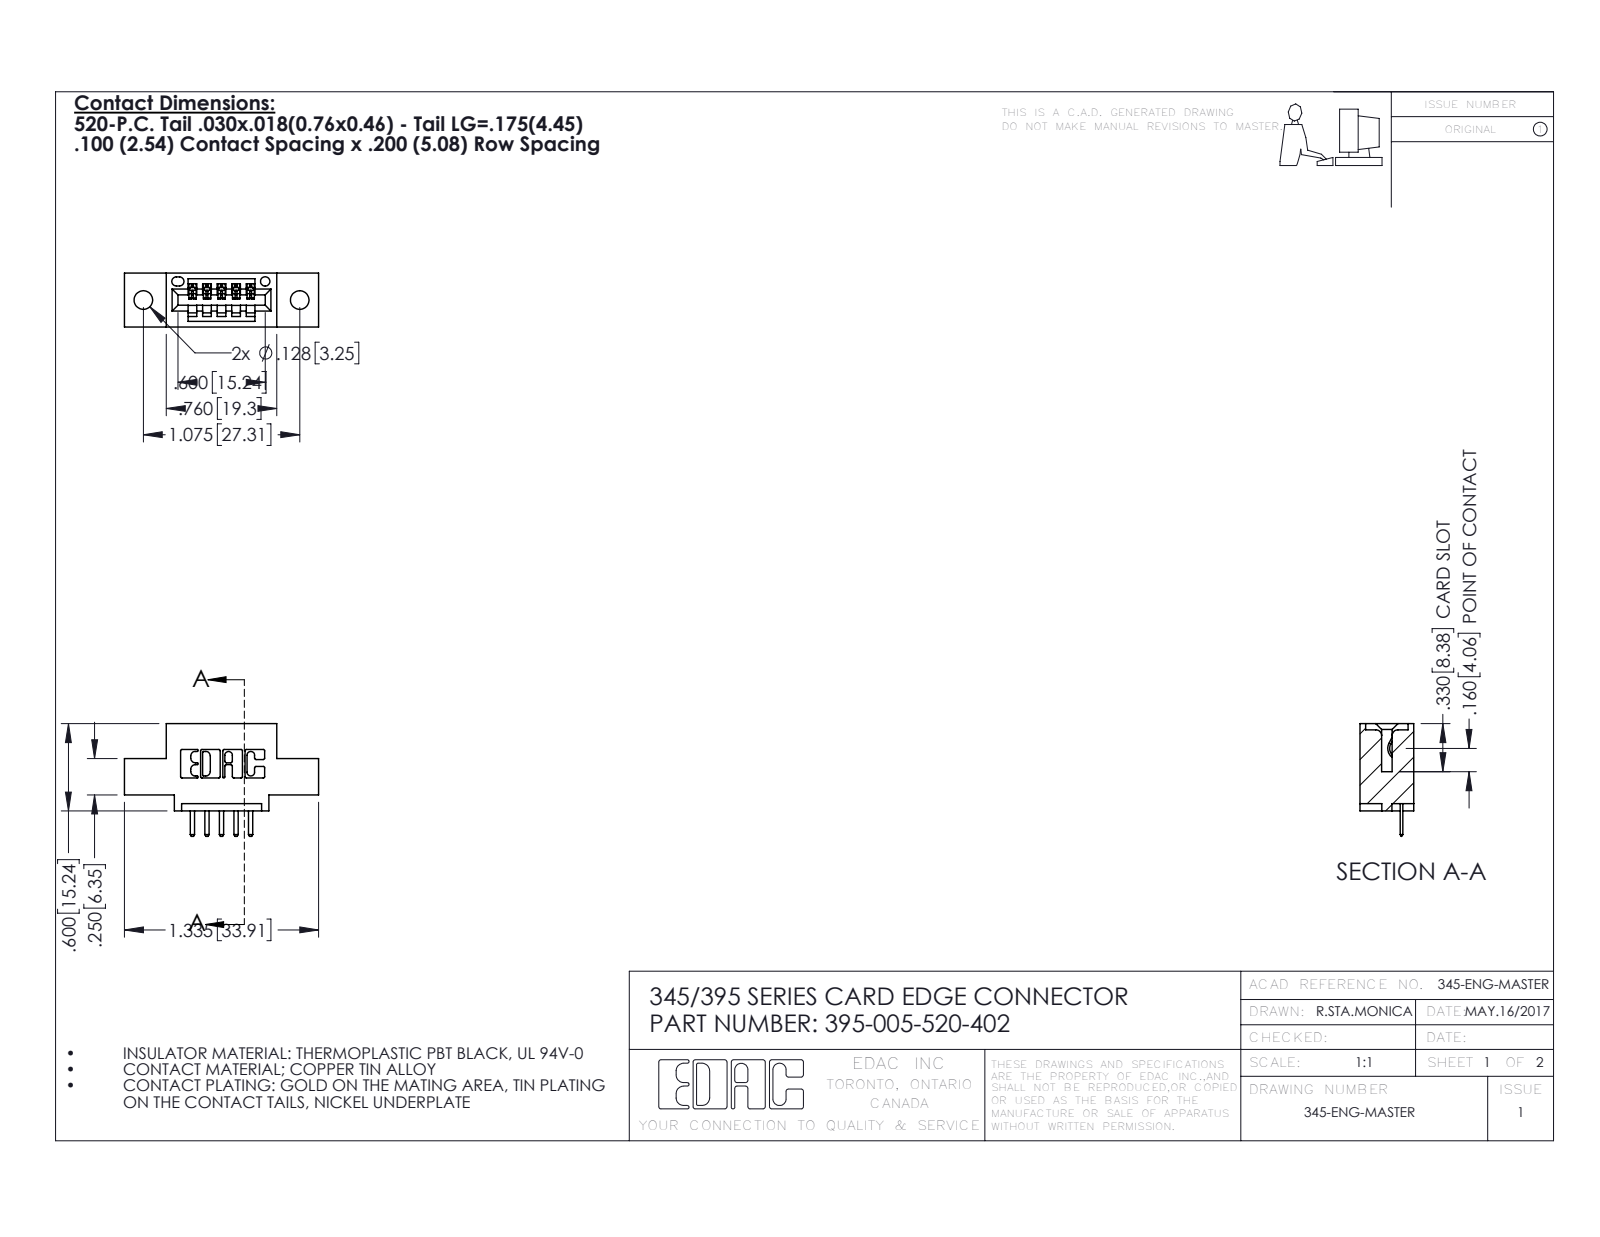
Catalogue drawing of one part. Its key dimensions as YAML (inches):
part_name: "395-005-520-402; 345-292-001_345-293-120; 345 Part_0.110 Offset - 0.128 Dia"
step_written_by: "SolidWorks 2016 (CONFIG_CONTROL_DESIGN)"
units: inches
bodies: {solids: 6, faces: 440, planar: 294, cylindrical: 146, other: 0}
overall_size: [1.335, 0.775, 0.37]
volume: 0.17
surface_area: 4.607
round_holes:
  - {diameter: 0.128, count: 2}
  - {diameter: 0.064, count: 1}
partial_cylinders:
  - {radius: 0.01, count: 22}
  - {radius: 0.01, count: 12}
  - {radius: 0.006, count: 10}
  - {radius: 0.007, count: 6}
  - {radius: 0.031, count: 6}
  - {radius: 0.026, count: 3}
  - {radius: 0.031, count: 2}
  - {radius: 0.04, count: 2}
face_to_face_distances: [0.37, 0.2, 0.1, 0.298, 0.072, 0.25, 0.025, 0.06, 0.16, 0.55]
hole_center_spacings: [0.27, 0.847, 1.075]
